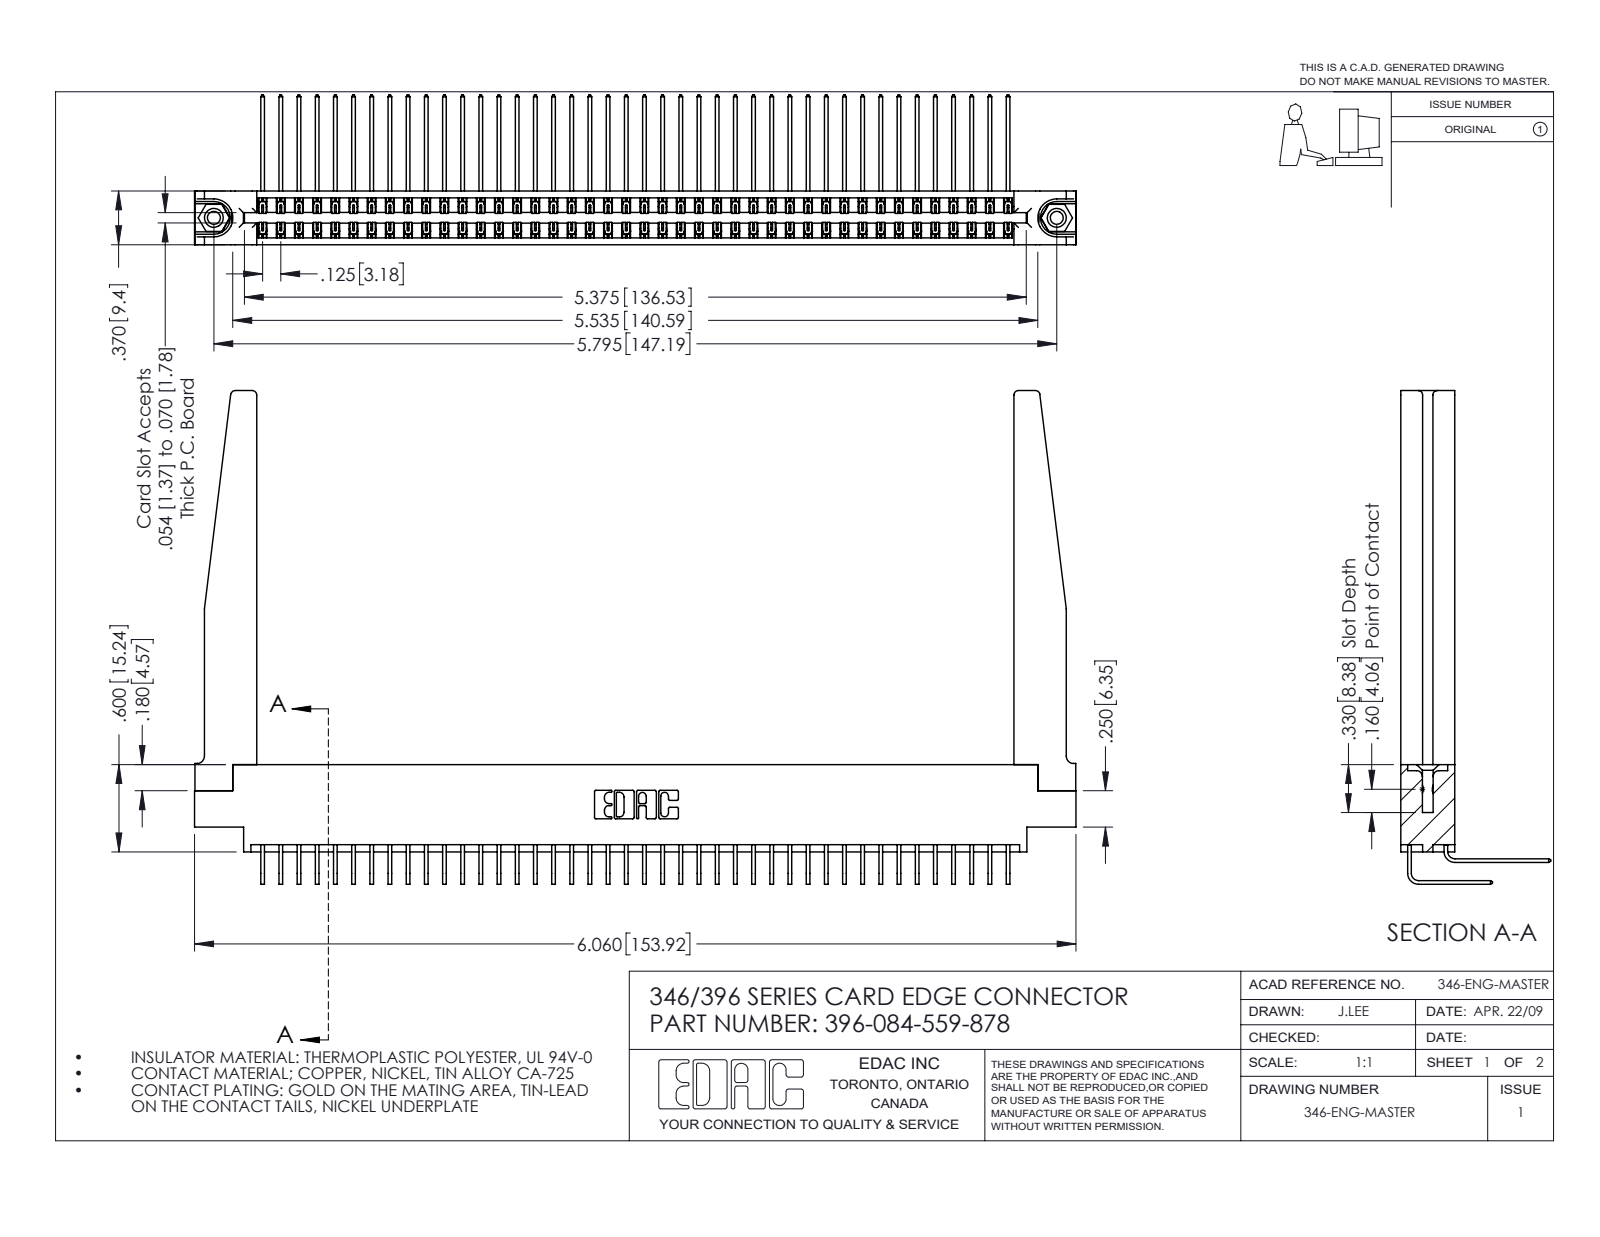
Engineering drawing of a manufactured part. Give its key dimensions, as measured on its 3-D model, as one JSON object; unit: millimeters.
{"part_name": "345-292-001_559 Tail - 2; 345-292-001_558 559 Tail - 1; 346 Part_0.170 Offset - 0.156 Dia-TH; 346-220-078_345-220-078 (+2 more)", "step_written_by": "SolidWorks 2016 (CONFIG_CONTROL_DESIGN)", "units": "millimeters", "bodies": {"solids": 89, "faces": 4896, "planar": 3330, "cylindrical": 1514, "other": 52}, "overall_size": [153.9, 86.2, 26.2], "volume_mm3": 22250, "surface_area_mm2": 30130, "round_holes": [[2.3, 2], [3.2, 2], [4, 2], [1.6, 1]], "round_bosses_or_shafts": [[3.9, 2]], "partial_cylinders_radius": [[0.2, 126], [0.3, 22], [0.8, 8], [0.2, 6], [0.8, 6], [1.3, 4], [0.7, 3], [0.4, 2]], "face_to_face_distances": [9.4, 1.2, 8.2, 1.8, 0.6, 6.4, 3.8, 3.8, 7.6, 7], "hole_center_spacings": [6.2, 141.9, 147.2]}
